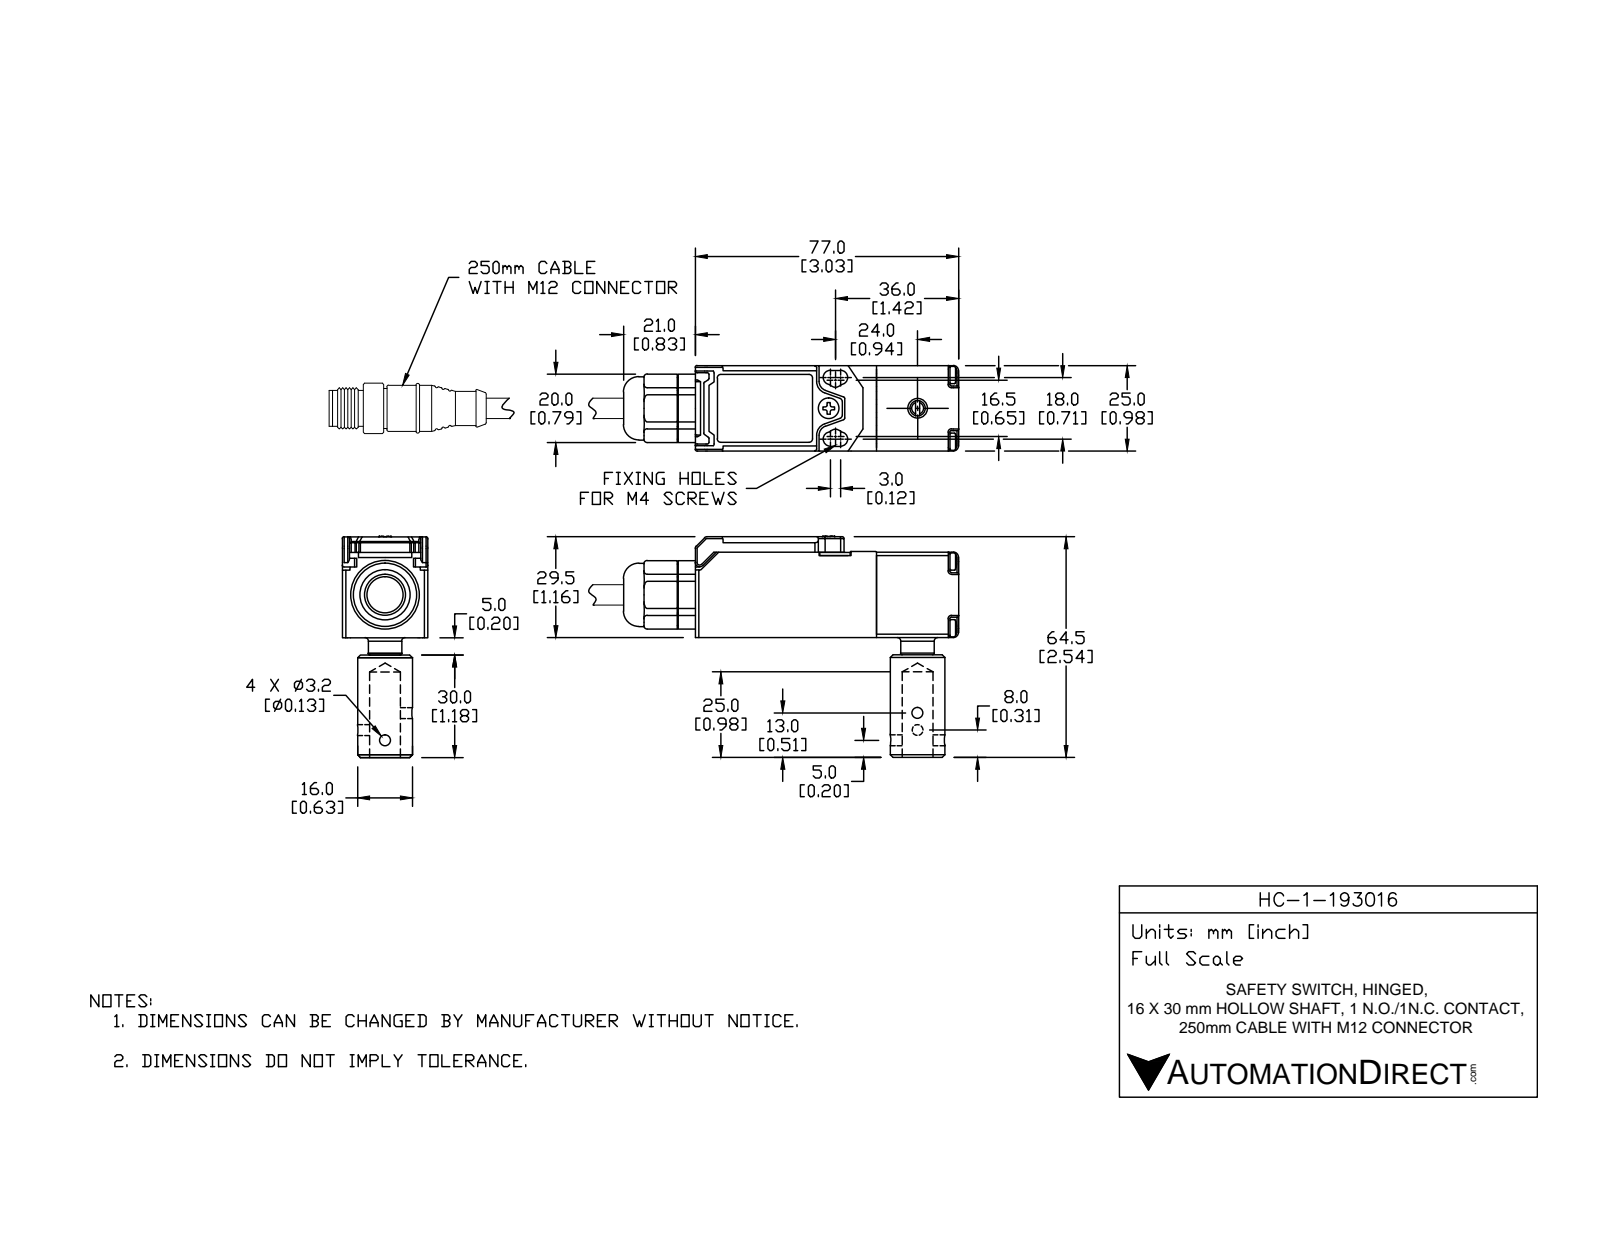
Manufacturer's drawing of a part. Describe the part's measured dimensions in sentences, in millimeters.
The part is named "HC-1-193016". Its 3-D file was written by "SolidWorks 2014 (AUTOMOTIVE_DESIGN)". It is 14 solids with 1716 faces: 700 planar, 611 cylindrical and 405 other. Overall it measures 80.5 by 64.7 by 25 millimeters. Its volume is 29 430 cubic millimeters and its surface area 28 750 square millimeters. Round holes: 8 of diameter 3.2, 4 of diameter 2.4, 2 of diameter 1.5, 2 of diameter 1.6, 2 of diameter 1.8, 2 of diameter 2.2, 2 of diameter 3.6, 1 of diameter 1.4, 1 of diameter 2.1, 1 of diameter 2.5, 1 of diameter 2.6, 1 of diameter 4.7. Round bosses or shafts: 5 of diameter 2.6, 4 of diameter 5, 4 of diameter 2, 2 of diameter 3.5, 1 of diameter 18.8, 1 of diameter 16, 1 of diameter 13.5, 1 of diameter 9.8. Partial cylindrical surfaces (rounded edges, fillets, slot ends): 226 of radius 0.5, 24 of radius 0.1, 20 of radius 0.3, 20 of radius 1, 7 of radius 1.5, 6 of radius 2.1, 6 of radius 2.8, 4 of radius 0.2. The main face-to-face distances are 25, 2, 1.8, 23.2, 1, 23, 24, 21, 22.2, 29.2. The hole center spacings are 13.8, 19.5, 4.3, 4.7, 6.2, 10.5, 10.7, 10.8.
